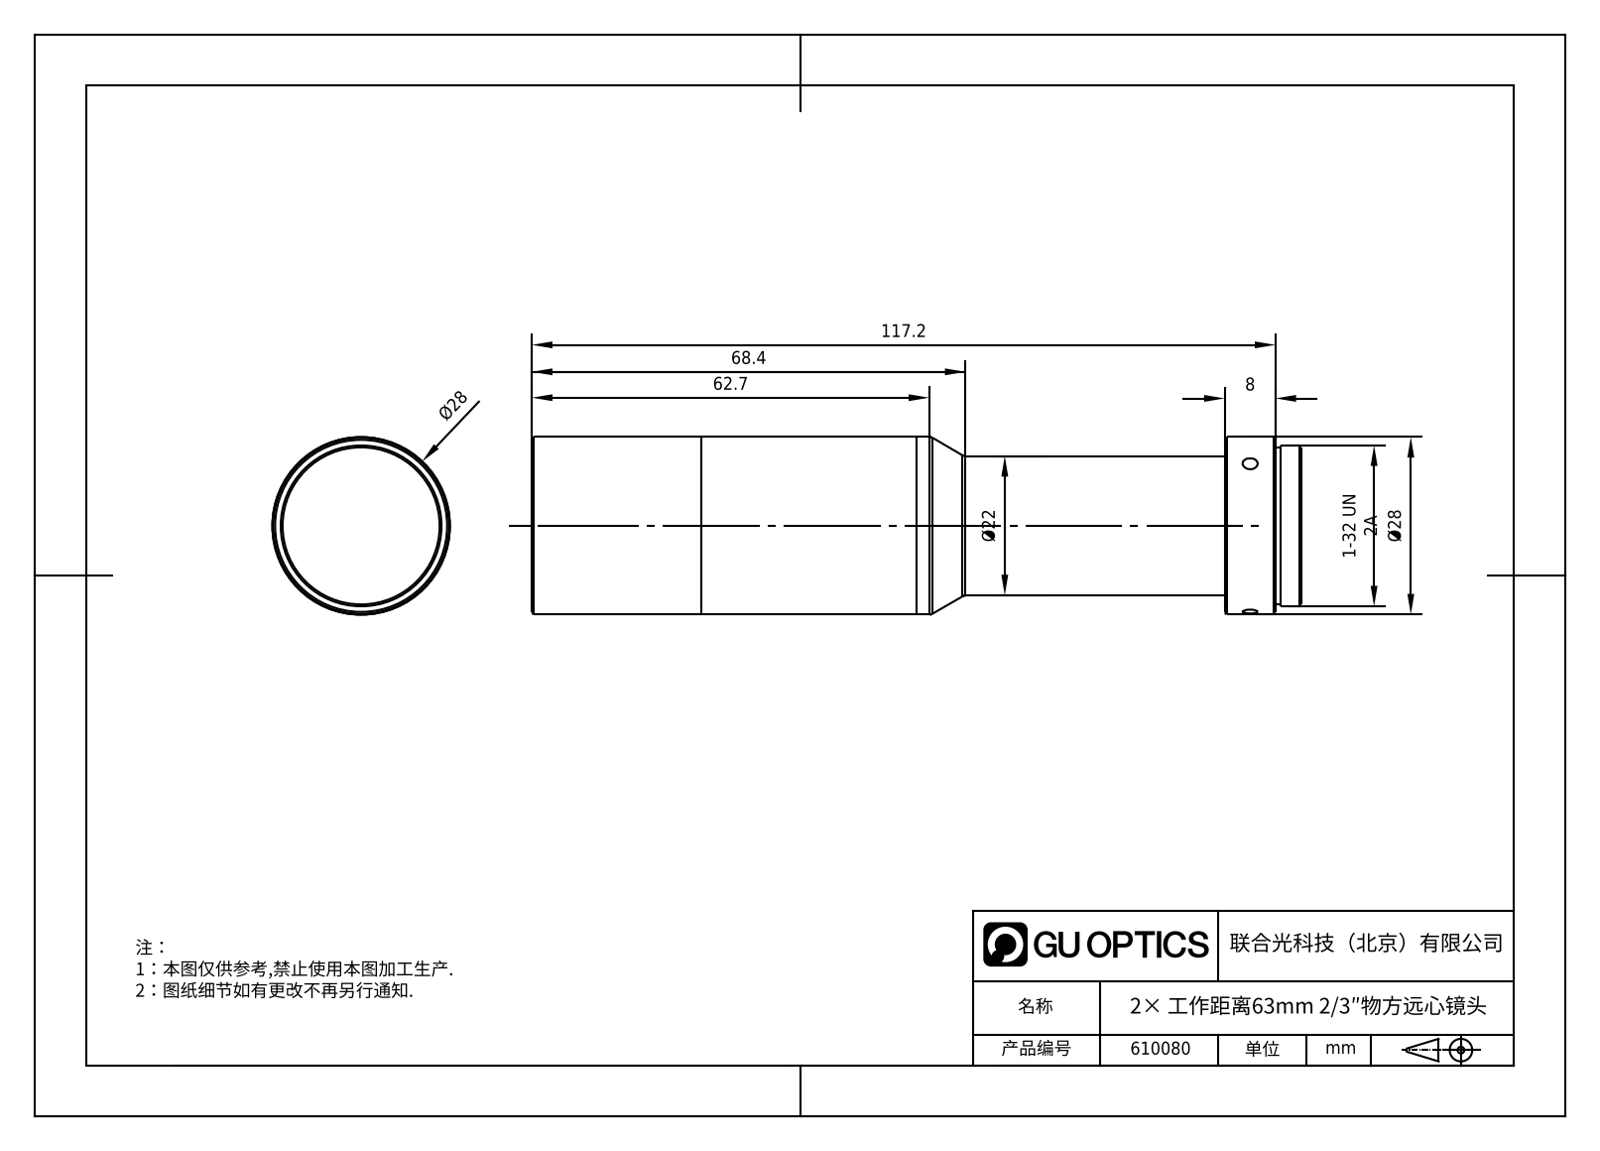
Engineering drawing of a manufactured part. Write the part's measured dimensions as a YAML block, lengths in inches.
part_name: "WWH20-63ATV3"
step_written_by: "SolidWorks 2017 (CONFIG_CONTROL_DESIGN)"
units: inches
bodies: {solids: 1, faces: 29, planar: 5, cylindrical: 10, other: 14}
overall_size: [4.772, 1.102, 1.102]
volume: 3.896
surface_area: 17.59
round_bosses_or_shafts:
  - {diameter: 1.102, count: 1}
  - {diameter: 1, count: 1}
  - {diameter: 0.961, count: 1}
  - {diameter: 0.866, count: 1}
face_to_face_distances: [4.772, 4.299, 0.472, 4.614, 0.315, 0.157, 4.646, 0.346, 0.031, 0.126]
